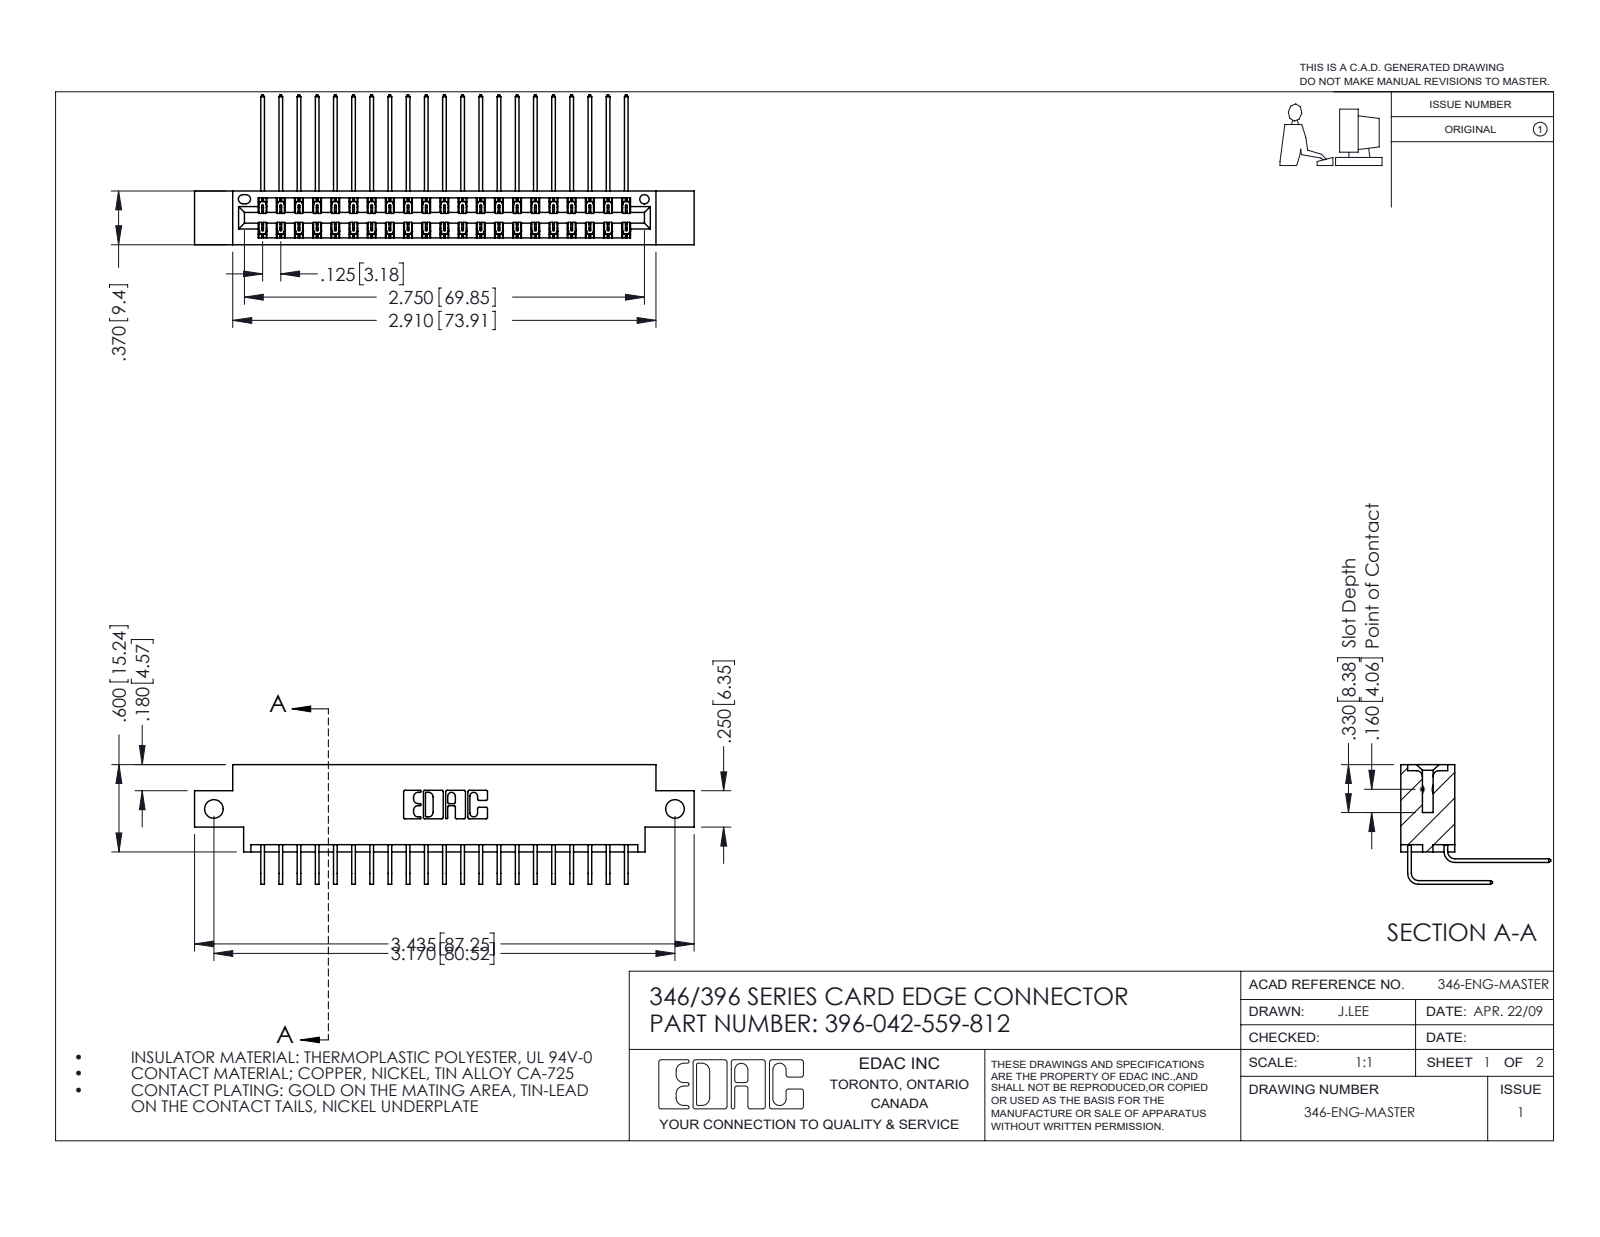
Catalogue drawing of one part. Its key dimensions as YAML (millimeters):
part_name: "345-292-001_559 Tail - 2; 345-292-001_558 559 Tail - 1; 396-042-559-812; 346 Part_0.170 Offset - Side Mount"
step_written_by: "SolidWorks 2016 (CONFIG_CONTROL_DESIGN)"
units: millimeters
bodies: {solids: 43, faces: 2394, planar: 1634, cylindrical: 760, other: 0}
overall_size: [87.2, 26.2, 20.9]
volume: 8340
surface_area: 12350
round_holes:
  - {diameter: 3.3, count: 2}
  - {diameter: 1.6, count: 1}
partial_cylinders:
  - {radius: 0.2, count: 63}
  - {radius: 0.3, count: 22}
  - {radius: 0.2, count: 6}
  - {radius: 0.8, count: 6}
  - {radius: 0.7, count: 3}
  - {radius: 0.4, count: 2}
  - {radius: 0.6, count: 2}
  - {radius: 0.6, count: 2}
face_to_face_distances: [1.2, 8.2, 9.4, 0.6, 6.4, 1.8, 7.6, 7, 3.8, 3.8]
hole_center_spacings: [80.5]
